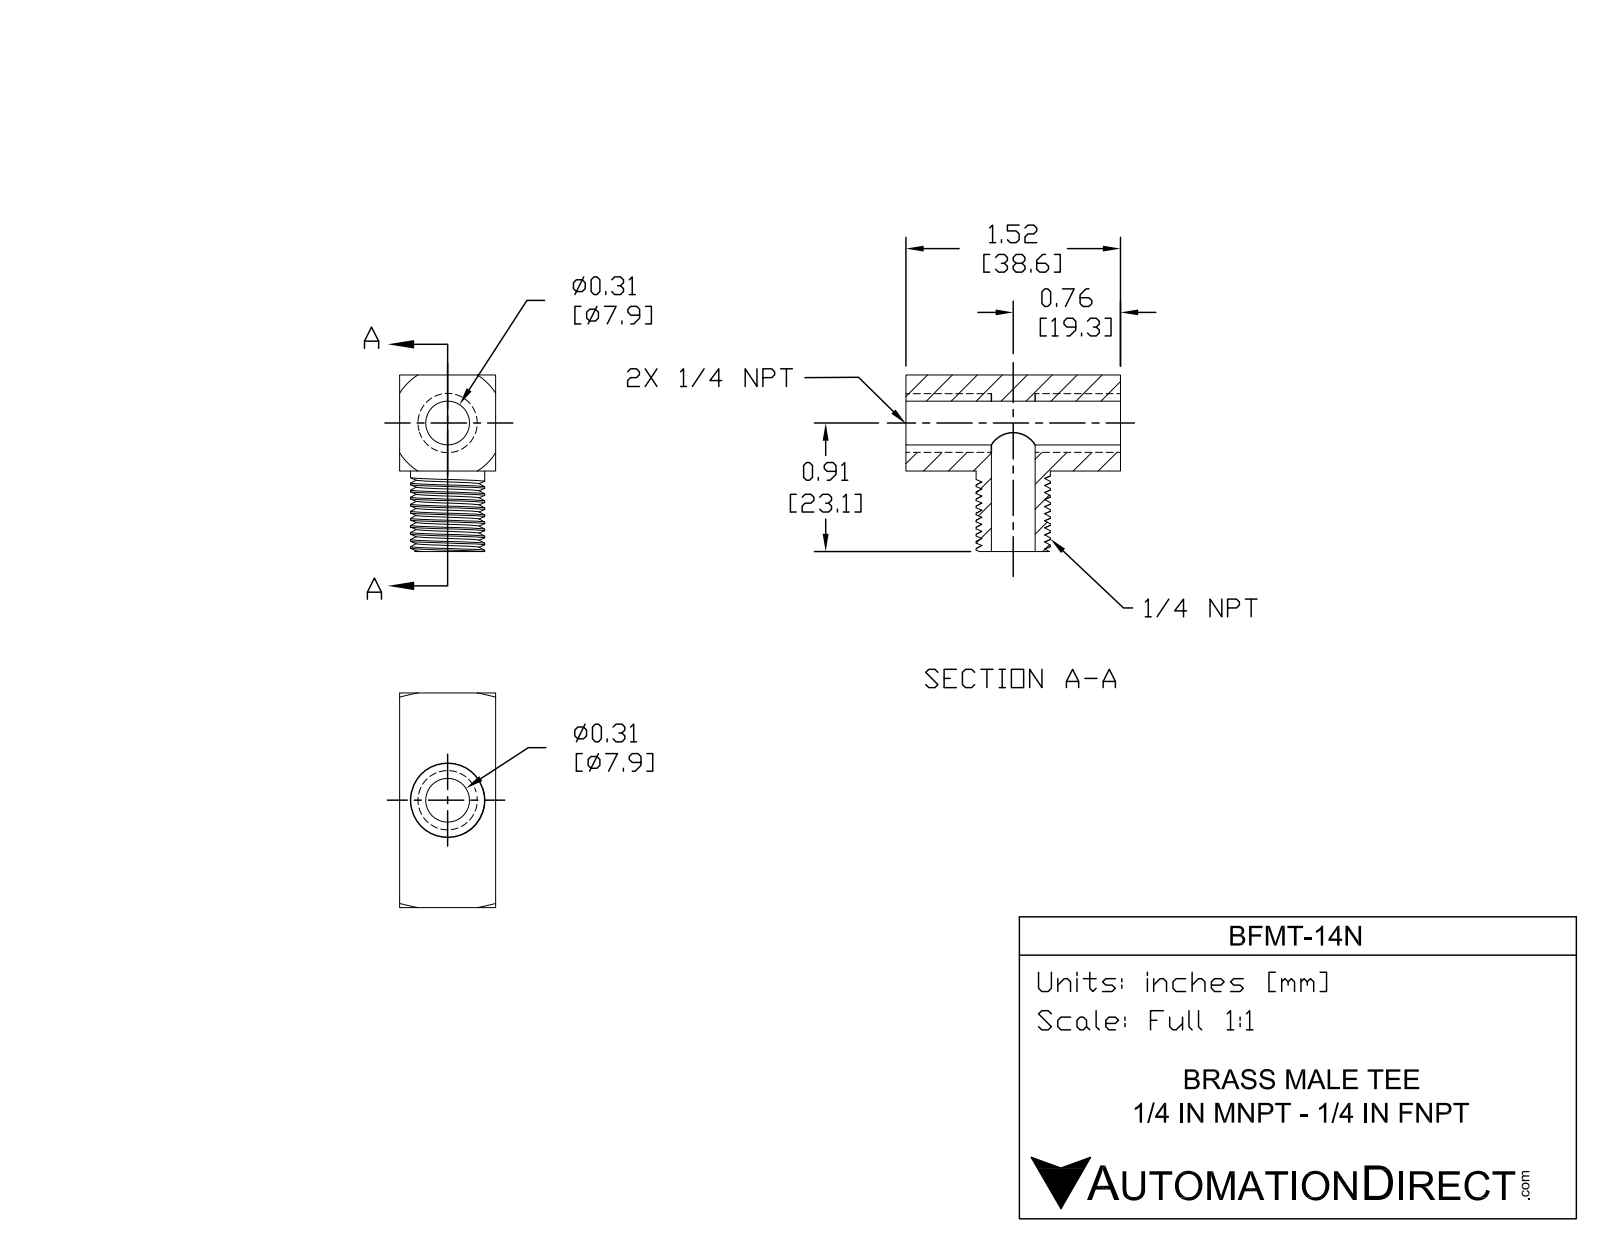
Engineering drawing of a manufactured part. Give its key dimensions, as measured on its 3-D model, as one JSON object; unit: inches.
{"part_name": "BFMT-14N", "step_written_by": "SolidWorks 2015 (CONFIG_CONTROL_DESIGN)", "units": "inches", "bodies": {"solids": 1, "faces": 46, "planar": 10, "cylindrical": 26, "other": 10}, "overall_size": [1.52, 1.25, 0.68], "volume_in3": 0.639, "surface_area_in2": 8.66, "round_holes": [[0.31, 2]], "round_bosses_or_shafts": [[0.525, 1]], "face_to_face_distances": [0.68, 1.52, 1.25, 0.57, 0.76, 0.76, 0.375, 0.305, 0.875]}
